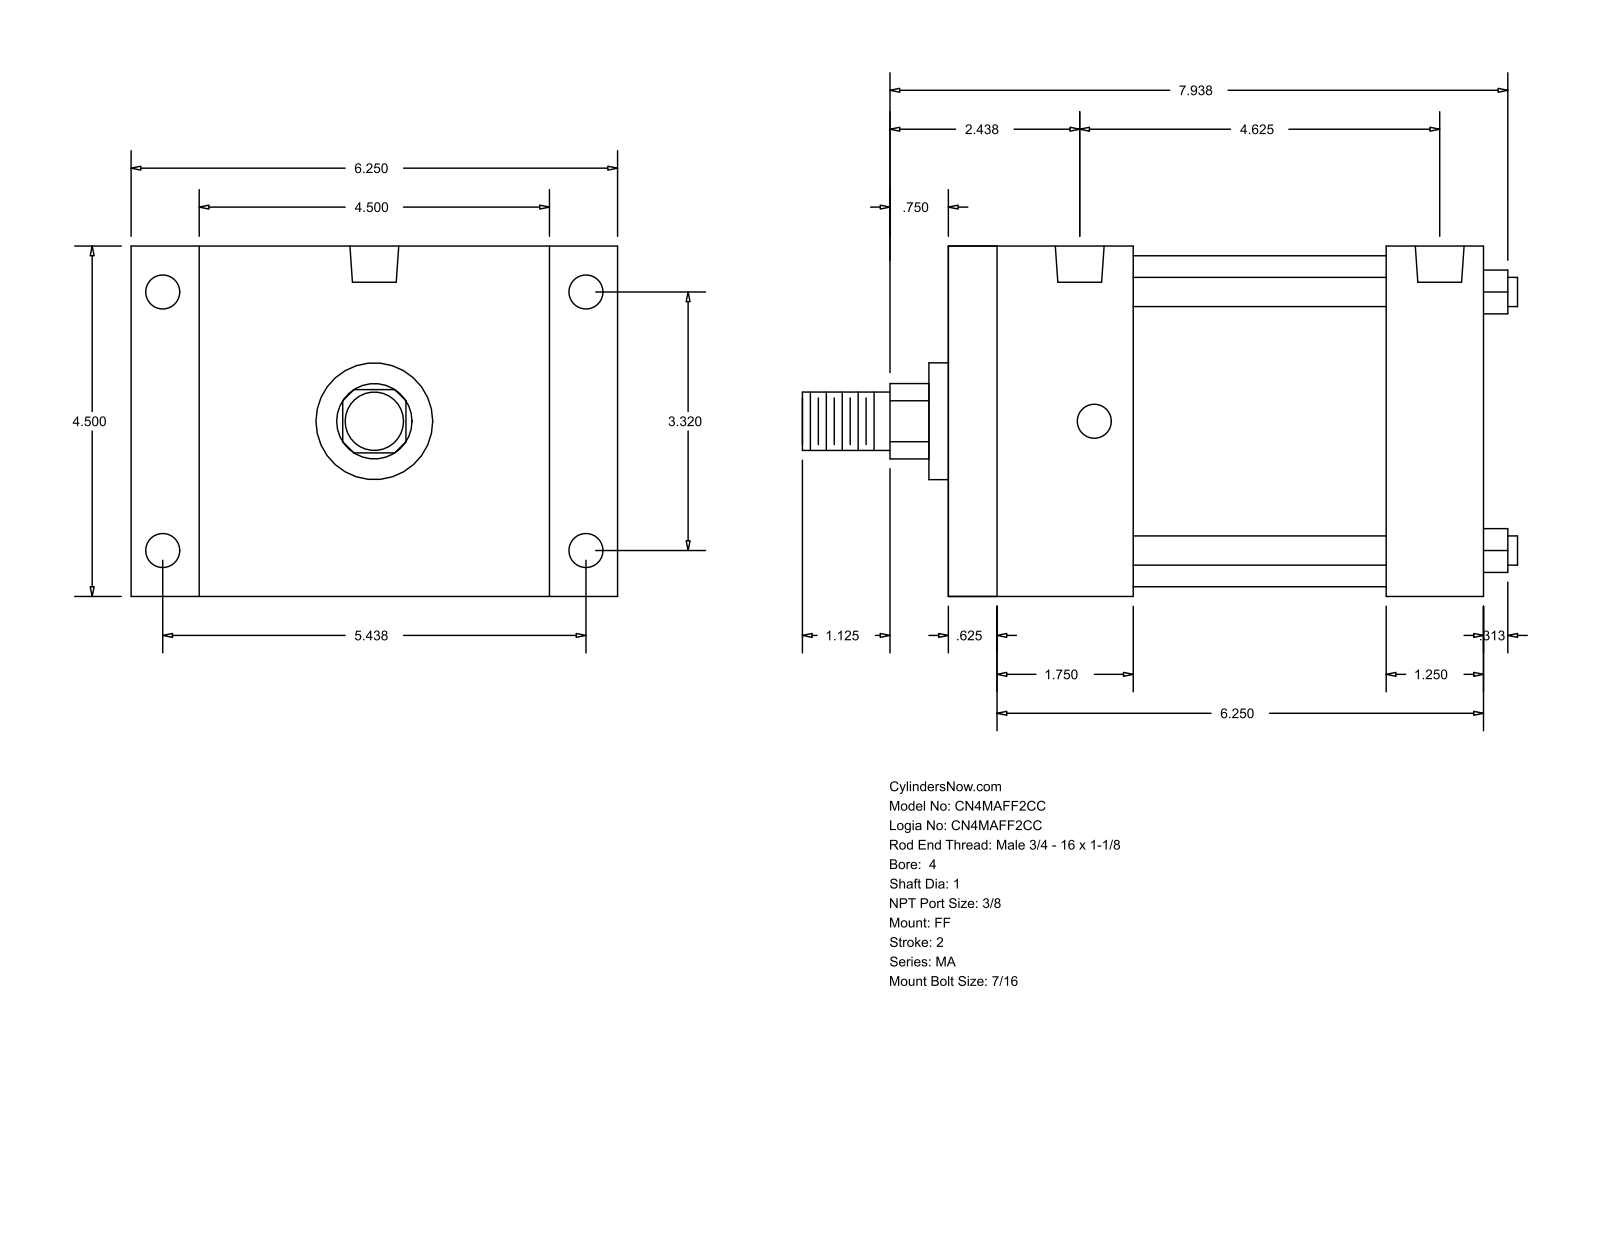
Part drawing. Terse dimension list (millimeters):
name: MA_FF__0400_1
written by: GSSL Pune (CONFIG_CONTROL_DESIGN)
unit: mm
bodies: 0 solids, 92 faces (64 planar, 28 cylindrical, 0 other)
size: 233.36 × 158.75 × 114.3
holes: 8× ⌀11.11, 2× ⌀15.93
bosses: 4× ⌀9.53, 1× ⌀107.95, 1× ⌀38.1, 1× ⌀25.4, 1× ⌀19.05
rounds: 1× R12.29
face distances: 114.3, 174.63, 158.76, 15.87, 22.23, 136.53, 142.88, 127.01, 31.75, 60.33
hole spacings: 84.32, 107.95, 138.12, 161.82, 4.76, 4.77, 112.71, 112.72
